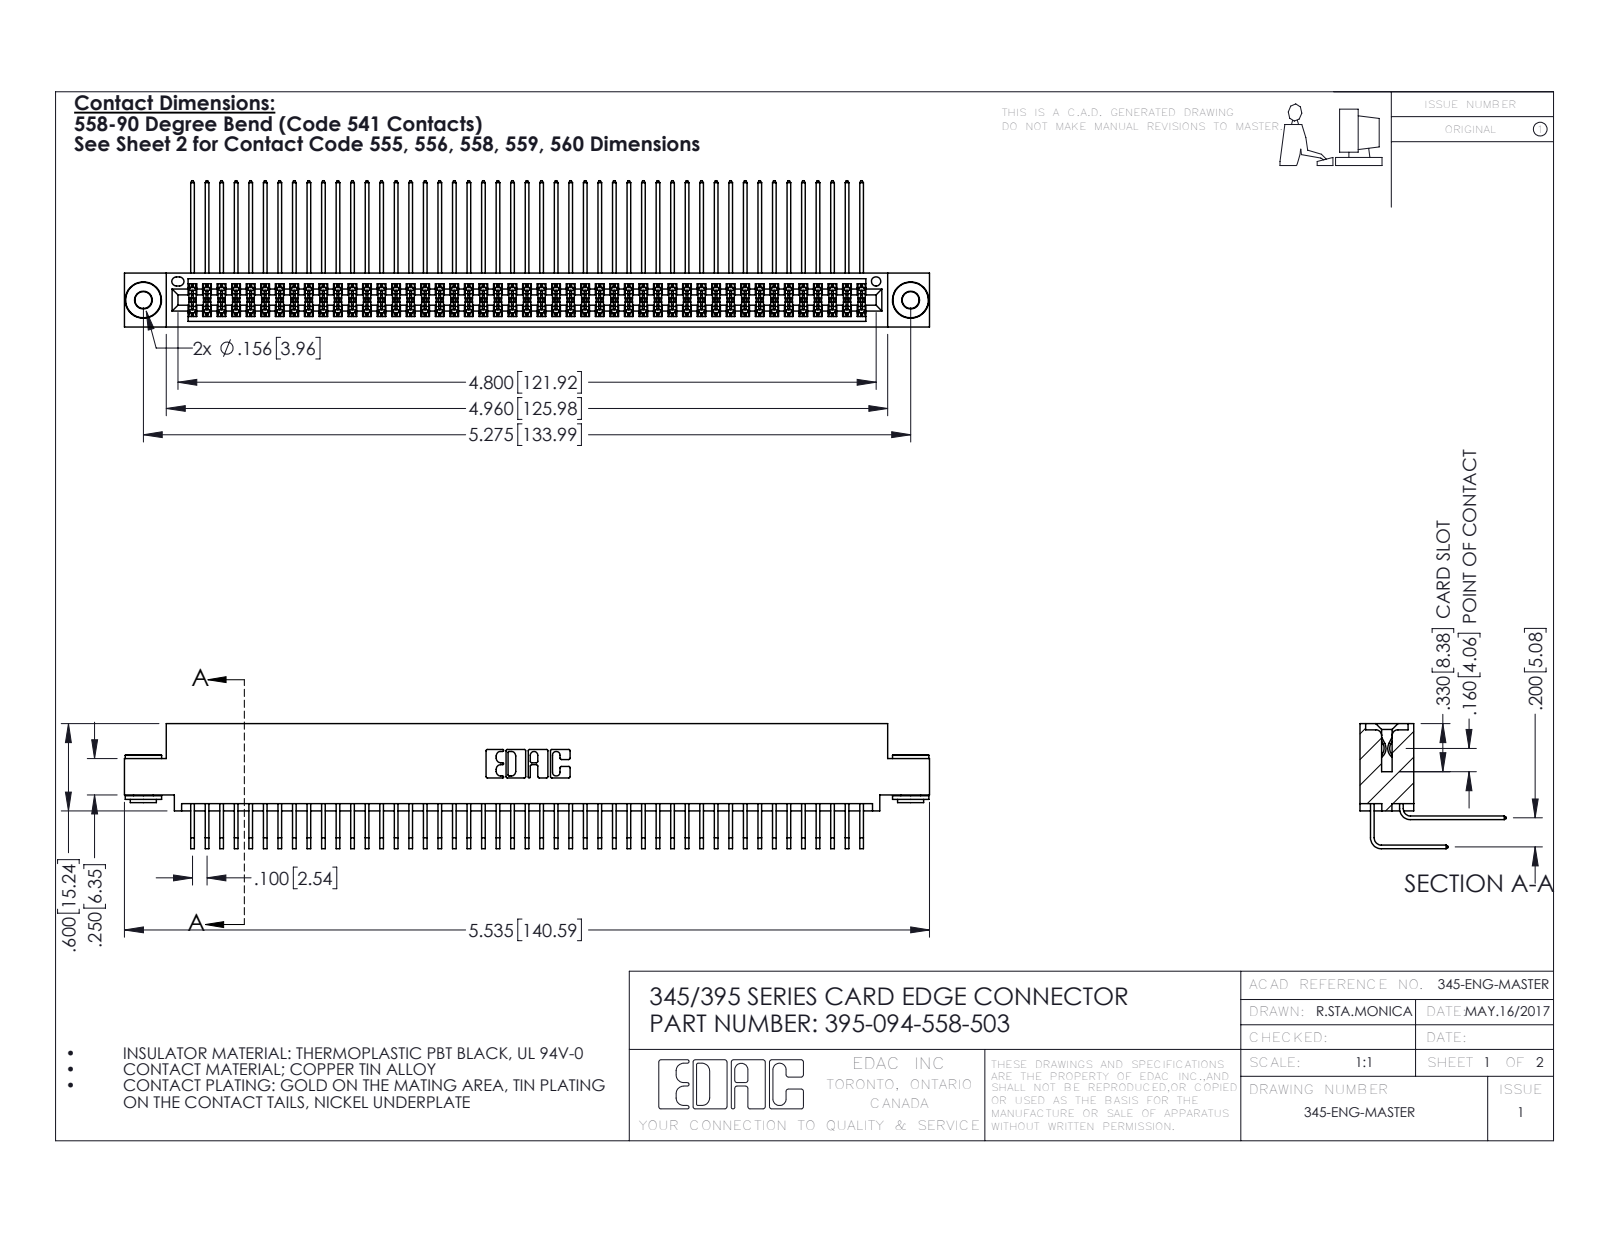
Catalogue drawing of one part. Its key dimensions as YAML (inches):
part_name: "395-094-558-503; 345 Part_0.110 Offset - 0.156 Dia-TH; 345-292-001_558 Tail - 2; 345-250-002_345-250-002-102 (+1 more)"
step_written_by: "SolidWorks 2016 (CONFIG_CONTROL_DESIGN)"
units: inches
bodies: {solids: 97, faces: 5056, planar: 3384, cylindrical: 1664, other: 8}
overall_size: [5.535, 1.005, 0.859]
volume: 0.866
surface_area: 37.08
round_holes:
  - {diameter: 0.116, count: 2}
  - {diameter: 0.156, count: 2}
  - {diameter: 0.064, count: 1}
round_bosses_or_shafts:
  - {diameter: 0.25, count: 2}
  - {diameter: 0.18, count: 2}
  - {diameter: 0.136, count: 2}
partial_cylinders:
  - {radius: 0.006, count: 142}
  - {radius: 0.01, count: 22}
  - {radius: 0.007, count: 6}
  - {radius: 0.031, count: 6}
  - {radius: 0.026, count: 3}
  - {radius: 0.014, count: 2}
  - {radius: 0.019, count: 2}
  - {radius: 0.022, count: 2}
face_to_face_distances: [0.072, 0.298, 0.2, 0.025, 0.37, 0.098, 0.272, 0.225, 0.025, 0.175]
hole_center_spacings: [0.27, 5.039, 5.275]
